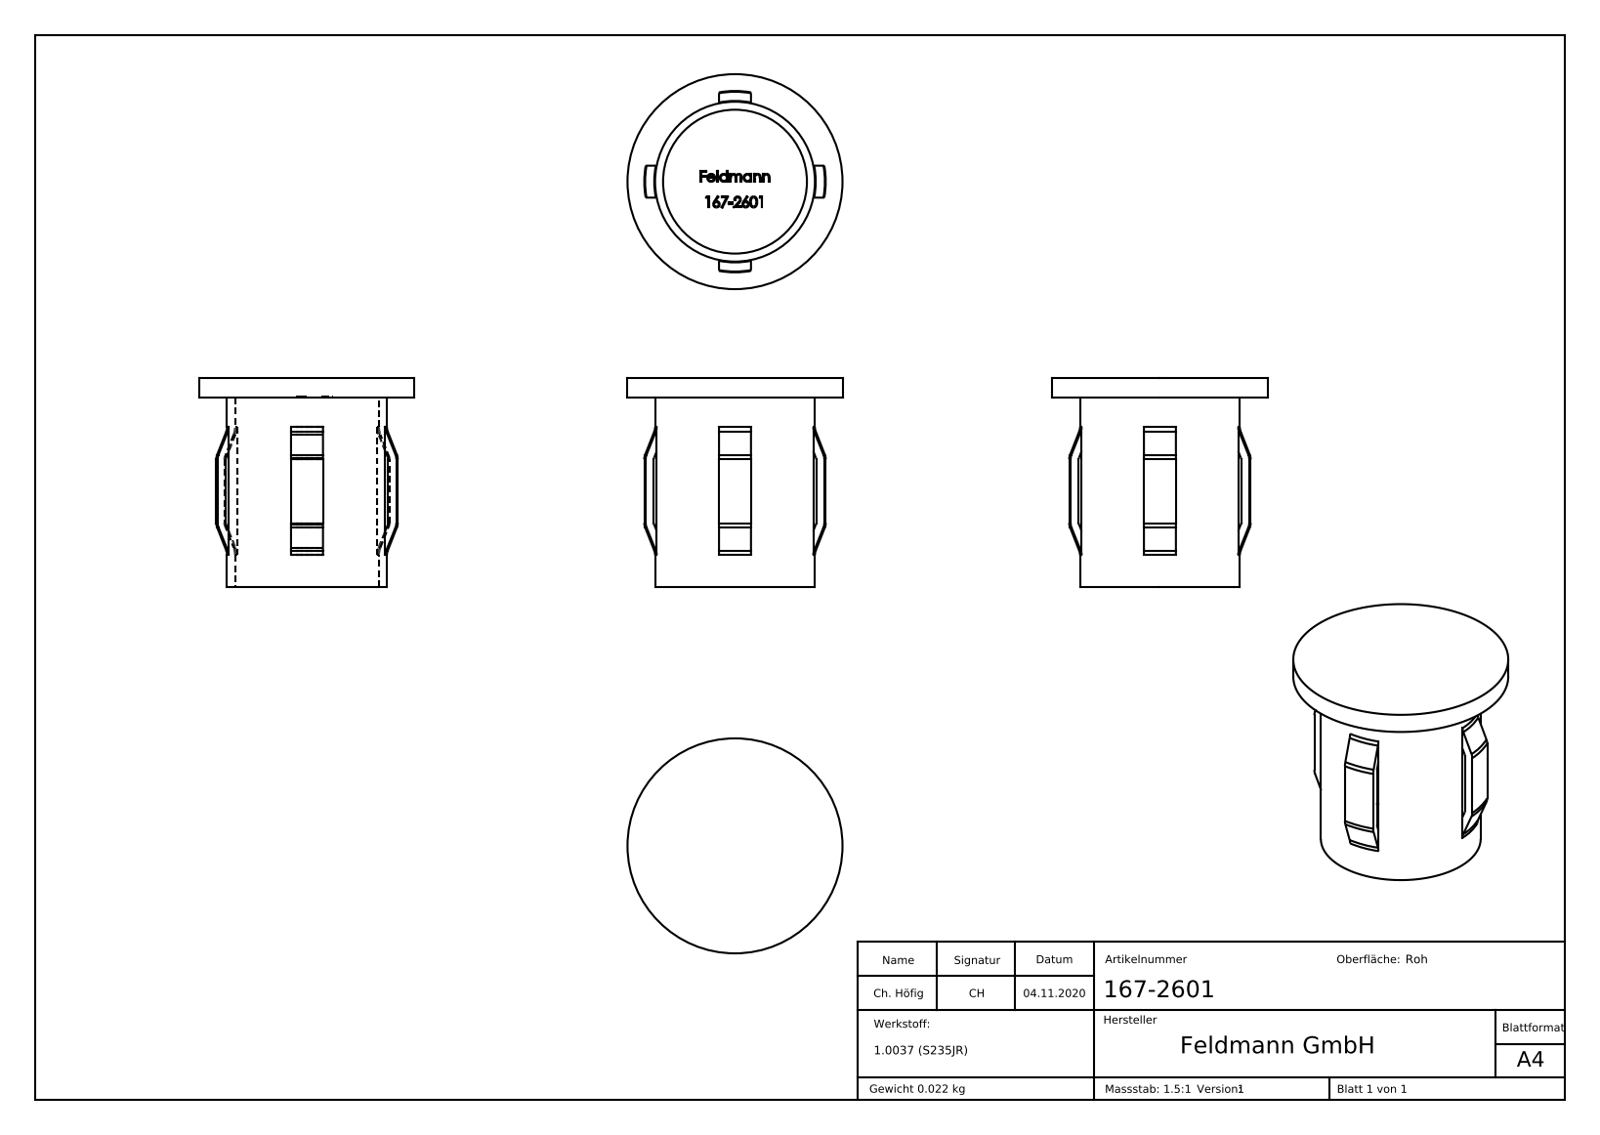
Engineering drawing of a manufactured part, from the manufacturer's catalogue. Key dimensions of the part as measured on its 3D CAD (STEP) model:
Part name (STEP PRODUCT): 167-2601
STEP written by: SolidWorks 2018 (CONFIG_CONTROL_DESIGN)
Units: millimetres
Bodies: 1 solid, 287 faces (130 planar, 16 cylindrical, 141 other)
Overall size (bounding box): 26.9 × 26.9 × 26.2
Volume: 2 842 mm³ · Surface area: 4 409 mm²
Round holes (diameter × count): ⌀18 ×1
Round bosses / shafts (diameter × count): ⌀26.9 ×1, ⌀20 ×1
Partial cylindrical surfaces — rounded edges, fillets, slot ends (radius × count): R10.35 ×1, R11.35 ×1
Main face-to-face distances: 2.5, 4, 23.7, 26.2, 2.4, 23.8, 2.97, 2, 0.39, 1.26
